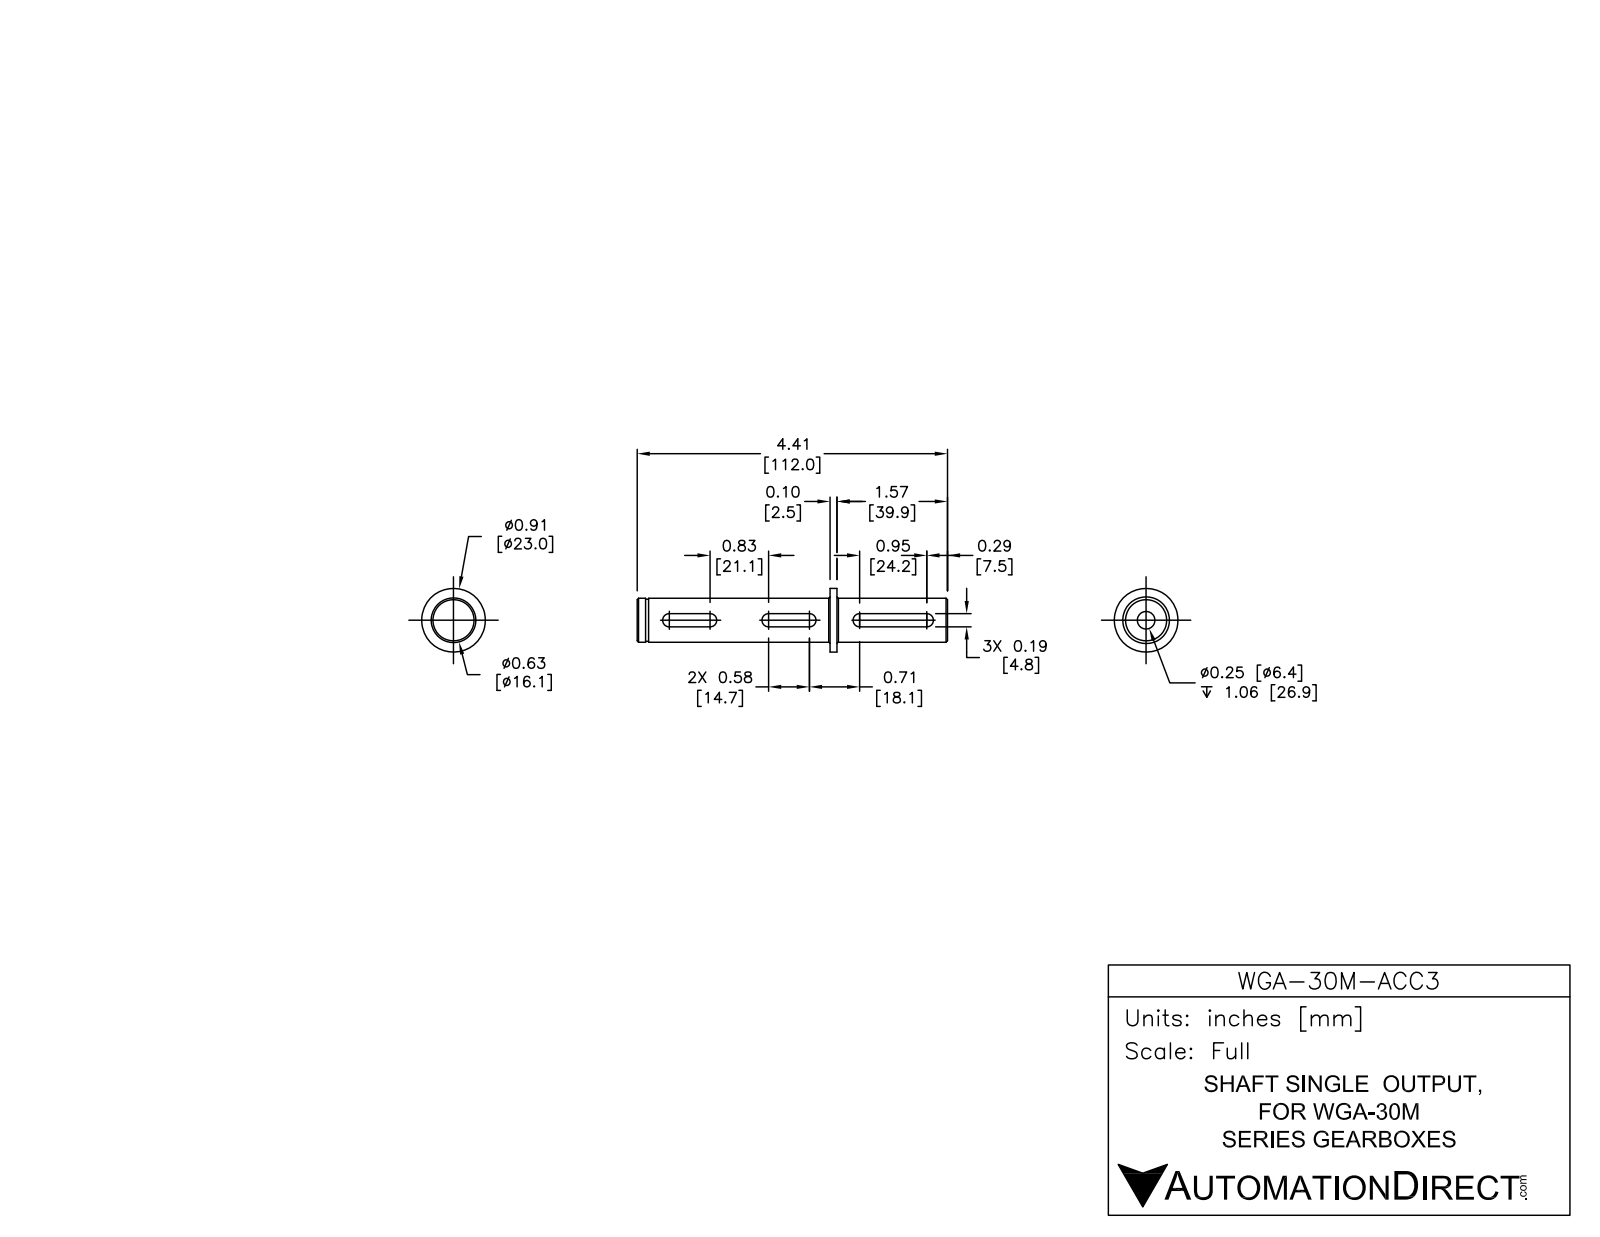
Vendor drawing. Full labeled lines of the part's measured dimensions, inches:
Part name (STEP PRODUCT): WGA-30M-ACC3
STEP written by: SolidWorks 2014 (AUTOMOTIVE_DESIGN)
Units: inches
Bodies: 1 solid, 43 faces (15 planar, 18 cylindrical, 10 other)
Overall size (bounding box): 4.409 × 0.906 × 0.906
Volume: 1.307 in³ · Surface area: 10.97 in²
Round holes (diameter × count): ⌀0.266 ×1
Round bosses / shafts (diameter × count): ⌀0.906 ×1, ⌀0.625 ×1, ⌀0.598 ×1
Partial cylindrical surfaces — rounded edges, fillets, slot ends (radius × count): R0.094 ×6
Main face-to-face distances: 0.098, 2.741, 2.839, 4.409, 1.669, 1.57, 0.187, 0.119, 0.162, 0.043
